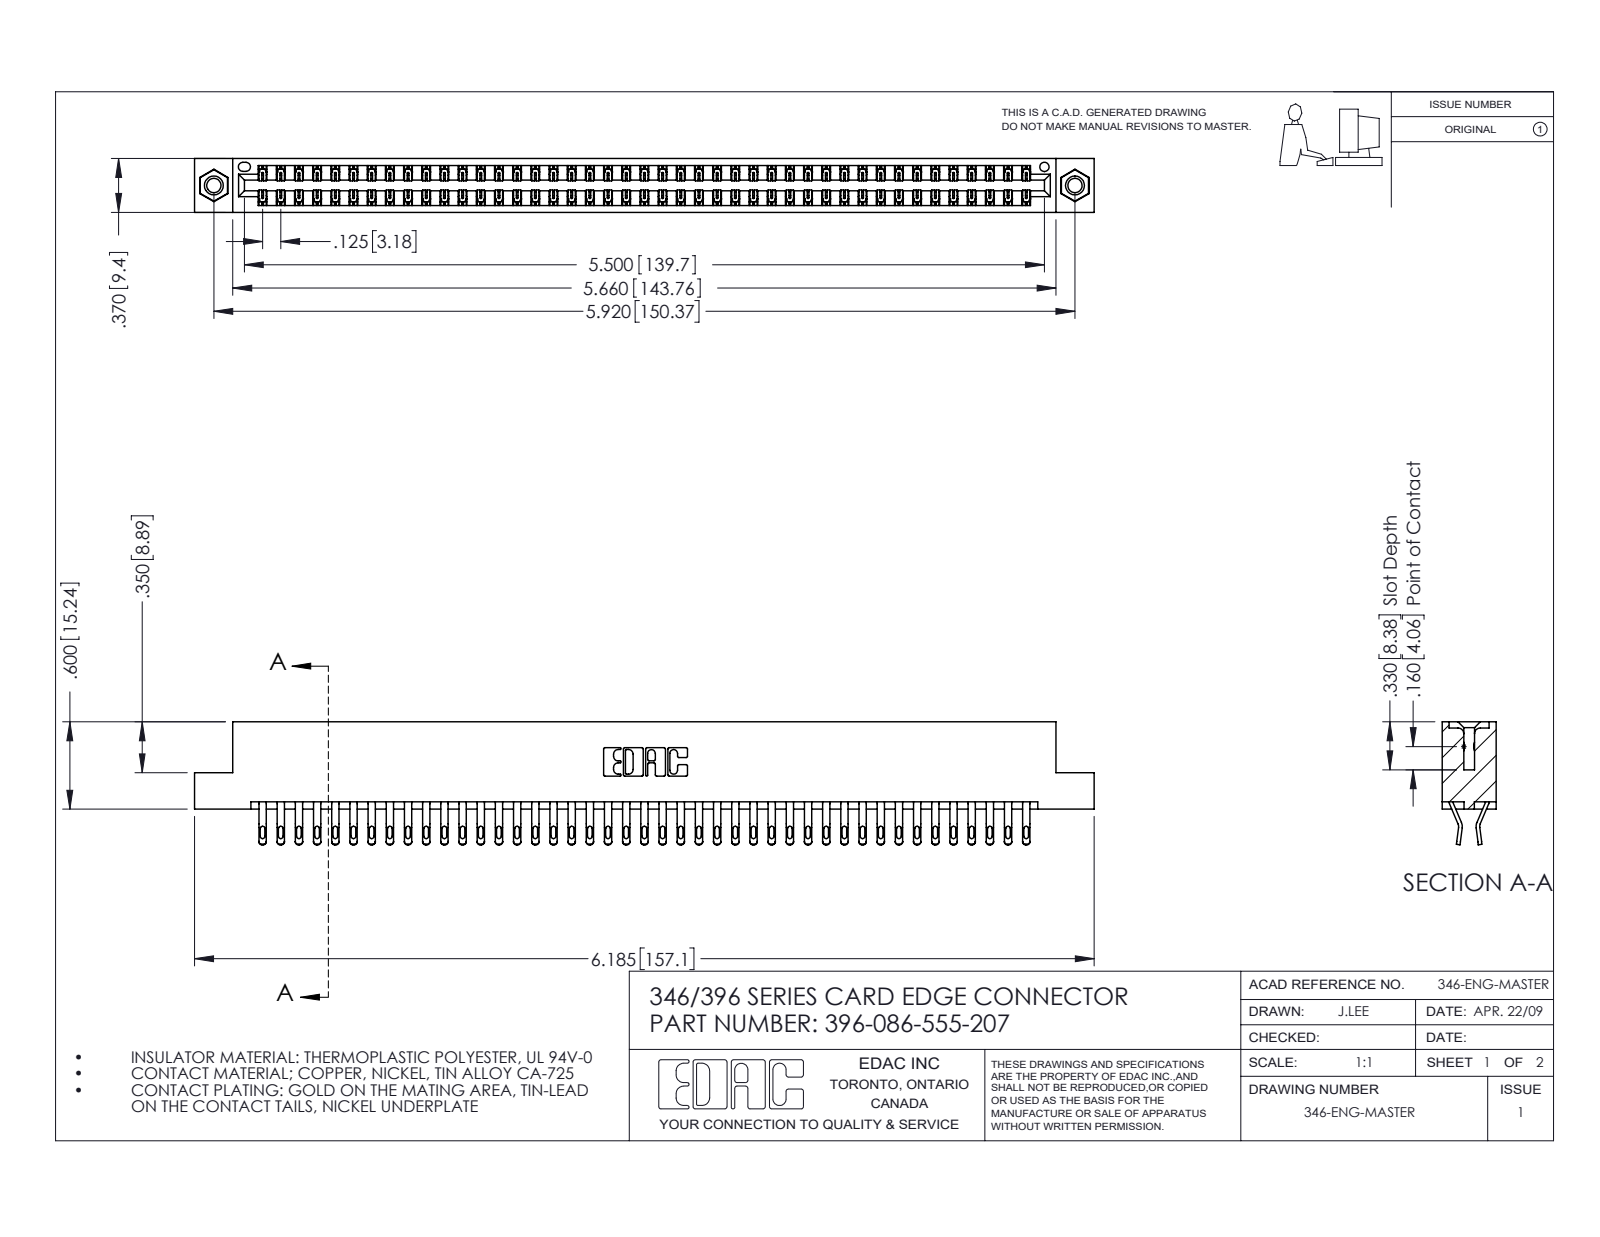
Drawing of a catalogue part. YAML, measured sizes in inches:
part_name: "346 Part_Flush Mounting Lugs - 0.156 Dia-TI; 345-250-001_345-250-005-103; 345-292-001_555 Tail; 396-086-555-207"
step_written_by: "SolidWorks 2016 (CONFIG_CONTROL_DESIGN)"
units: inches
bodies: {solids: 89, faces: 5170, planar: 2946, cylindrical: 2208, other: 16}
overall_size: [6.185, 0.845, 0.37]
volume: 0.95
surface_area: 34.61
round_holes:
  - {diameter: 0.098, count: 2}
  - {diameter: 0.125, count: 2}
  - {diameter: 0.156, count: 2}
  - {diameter: 0.064, count: 1}
round_bosses_or_shafts:
  - {diameter: 0.155, count: 2}
partial_cylinders:
  - {radius: 0.016, count: 172}
  - {radius: 0.02, count: 172}
  - {radius: 0.006, count: 129}
  - {radius: 0.01, count: 22}
  - {radius: 0.007, count: 6}
  - {radius: 0.031, count: 6}
  - {radius: 0.026, count: 3}
  - {radius: 0.01, count: 2}
face_to_face_distances: [0.048, 0.322, 0.37, 0.25, 0.025, 0.072, 0.298, 0.275, 0.148, 0.222]
hole_center_spacings: [0.246, 5.711, 5.92]
